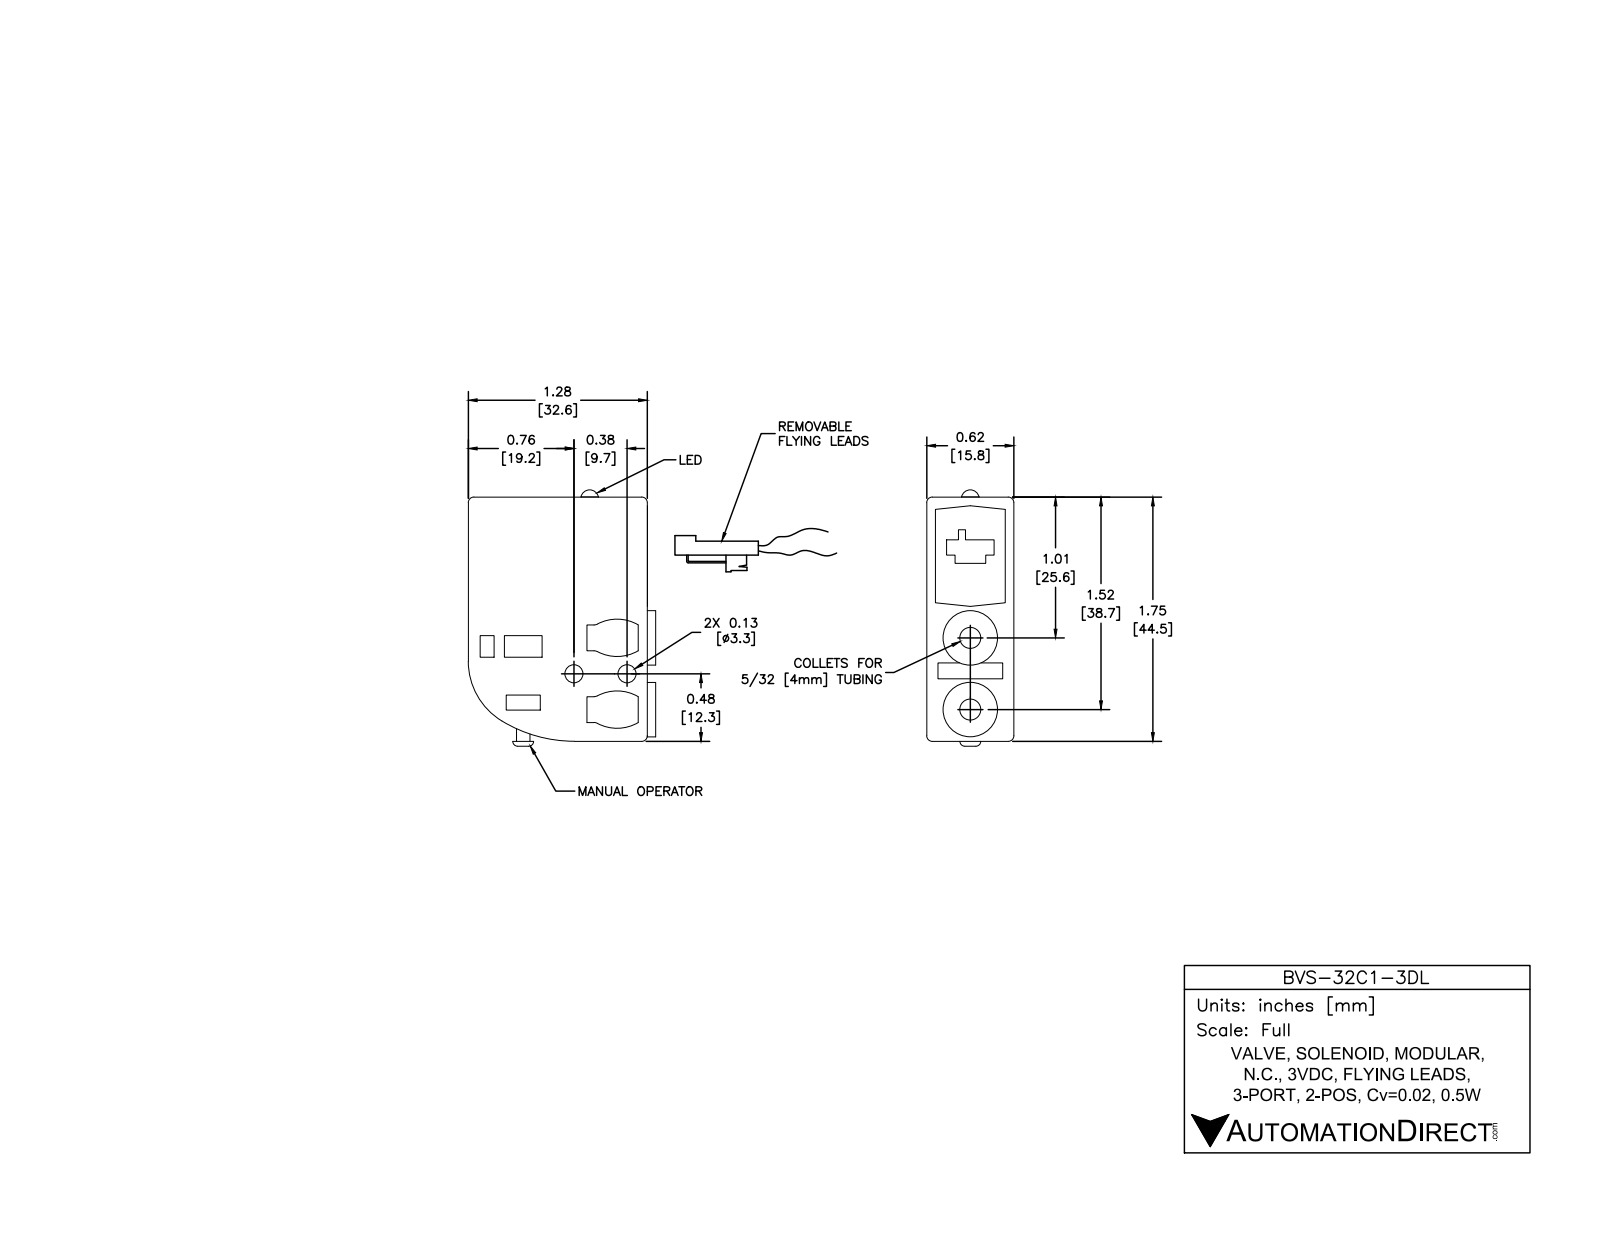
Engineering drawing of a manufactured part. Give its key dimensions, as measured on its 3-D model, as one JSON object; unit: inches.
{"part_name": "BVS-32C1-3DL", "step_written_by": "SolidWorks 2016 (AUTOMOTIVE_DESIGN)", "units": "inches", "bodies": {"solids": 1, "faces": 149, "planar": 83, "cylindrical": 54, "other": 12}, "overall_size": [1.84, 1.788, 0.62], "volume_in3": 1.259, "surface_area_in2": 10.37, "round_holes": [[0.13, 2], [0.15, 2], [0.25, 2], [0.05, 1]], "round_bosses_or_shafts": [[0.06, 6], [0.39, 2], [0.1, 1]], "partial_cylinders_radius": [[0.05, 4], [0.3, 4], [0.04, 3], [0.5, 1], [1, 1]], "face_to_face_distances": [0.62, 0.1, 1.29, 0.52, 1.291, 1.75, 1, 0.15, 0.06, 1.35], "hole_center_spacings": [0.06, 0.38, 0.45, 0.51]}
